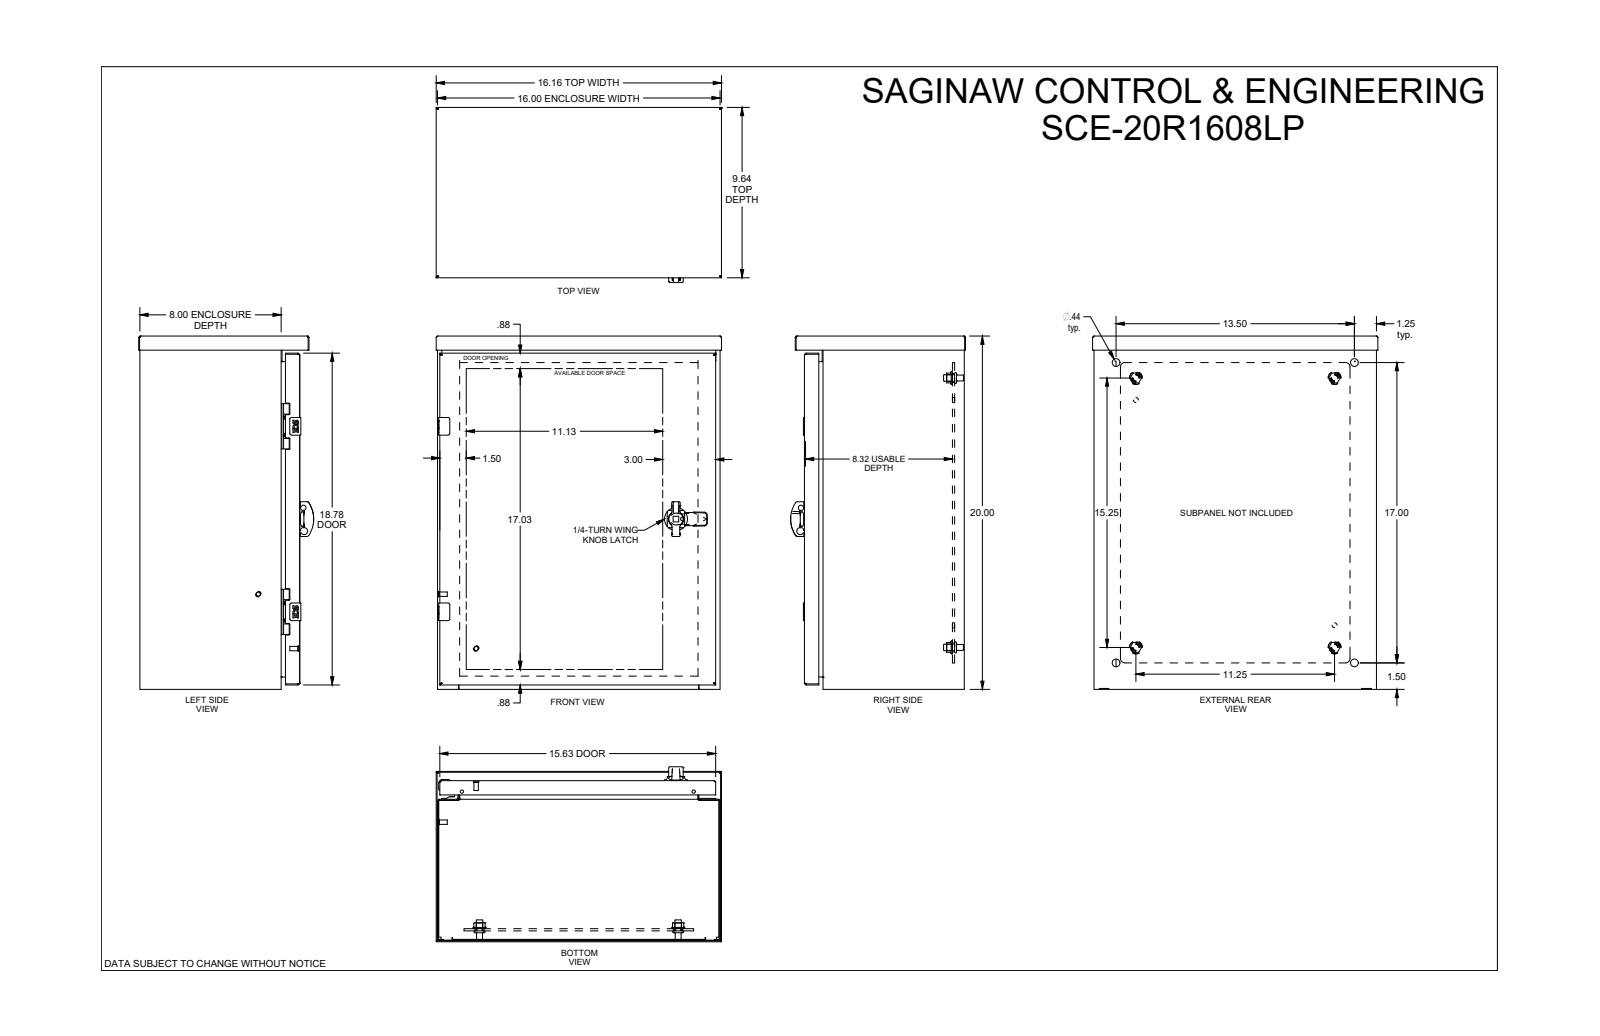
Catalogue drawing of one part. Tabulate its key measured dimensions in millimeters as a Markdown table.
| quantity | value |
| --- | --- |
| part name | SCE-20R1608LP |
| STEP written by | SolidWorks 2019 (CONFIG_CONTROL_DESIGN) |
| units | millimeters |
| bodies | 0 solids, 1908 faces (872 planar, 664 cylindrical, 372 other) |
| overall size | 508 × 410.4 × 251.6 |
| round holes (diameter × count) | 4.4 × 4, 5.2 × 4, 6.2 × 4, 6.8 × 4, 9.3 × 4, 9.5 × 4, 11.1 × 4, 12.7 × 4, 1 × 2, 4 × 2, 4.8 × 2, 5.5 × 2 |
| round bosses / shafts (diameter × count) | 4.3 × 6, 9.3 × 4, 8.4 × 4, 6.4 × 4, 6.1 × 4, 5 × 3, 6.3 × 2, 33.1 × 1 |
| partial cylindrical surfaces (radius × count) | 0.4 × 70, 0.3 × 30, 0.3 × 28, 1.2 × 16, 2.4 × 16, 0.8 × 15, 0.5 × 12, 0.8 × 10 |
| main face-to-face distances | 1.2, 227.2, 228.4, 405.2, 1.5, 229.9, 228.7, 506.8, 12.7, 17.1 |
| hole center spacings | 266.7, 36.2, 315.1, 410.6, 516.3, 0.4, 0.4, 12.3 |
